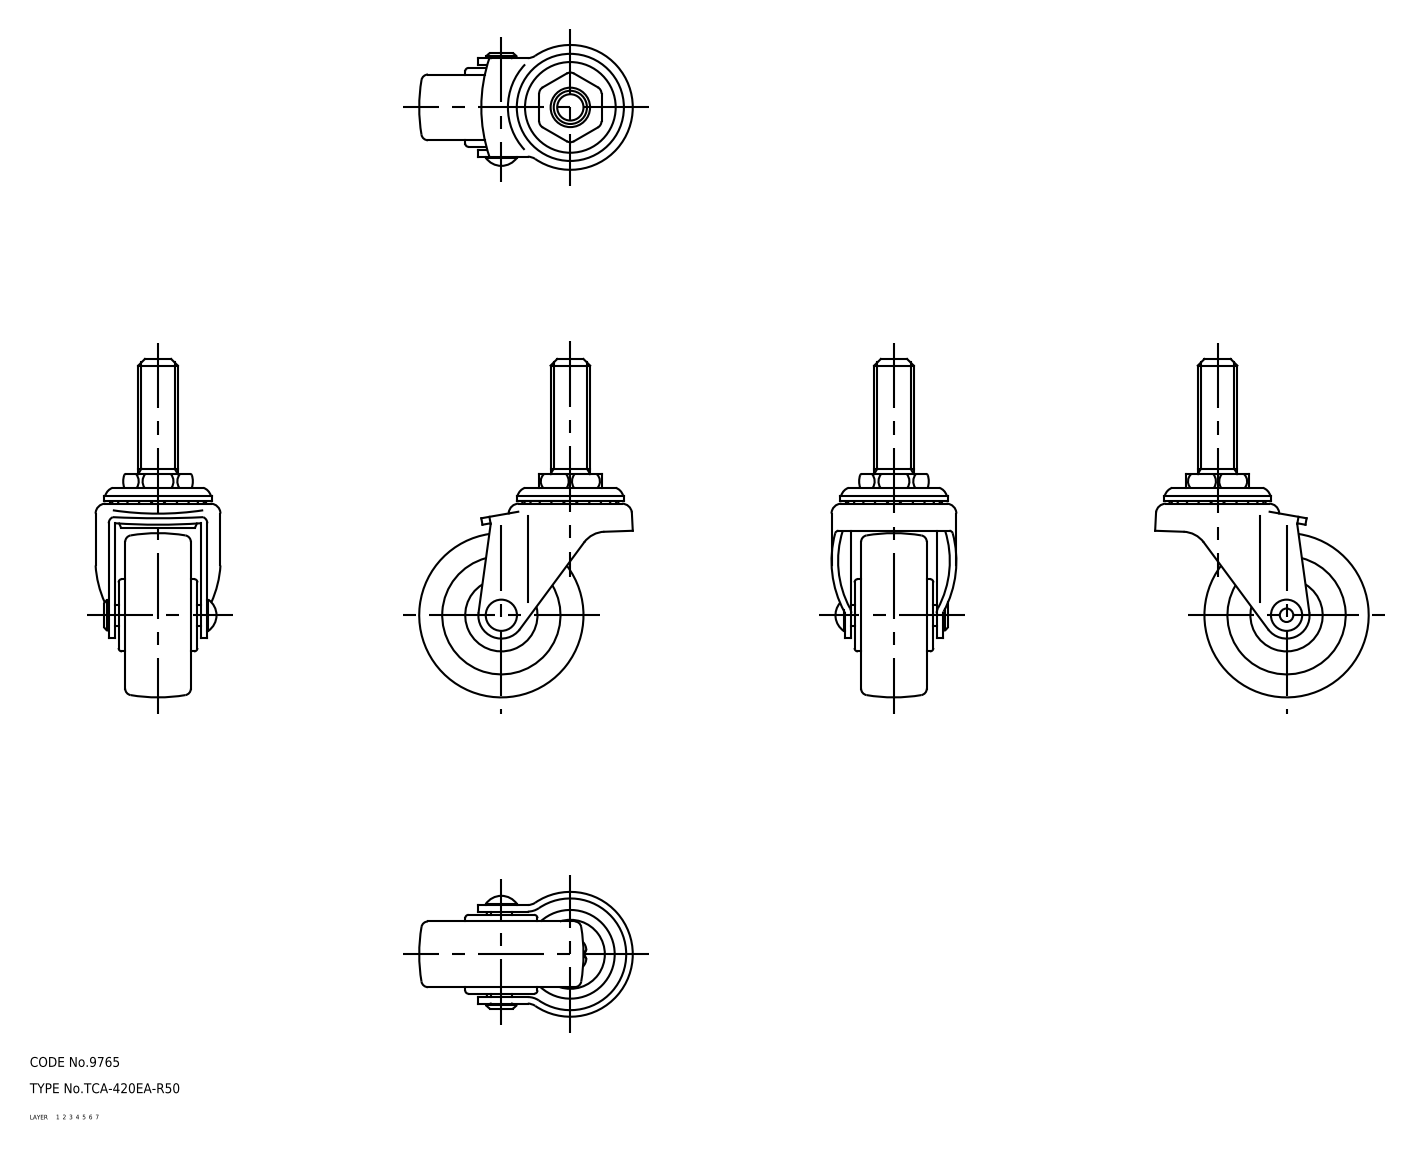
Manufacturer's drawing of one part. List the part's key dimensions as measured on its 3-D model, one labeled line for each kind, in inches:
Part name (STEP PRODUCT): wheel; mounting plate; main shaft; axle (+1 more)
STEP written by: CADfix (AUTOMOTIVE_DESIGN)
Units: inches
Bodies: 5 solids, 217 faces (0 planar, 0 cylindrical, 217 other)
Overall size (bounding box): 4.055 × 2.575 × 1.496
Volume: 3.456 in³ · Surface area: 33.58 in²
